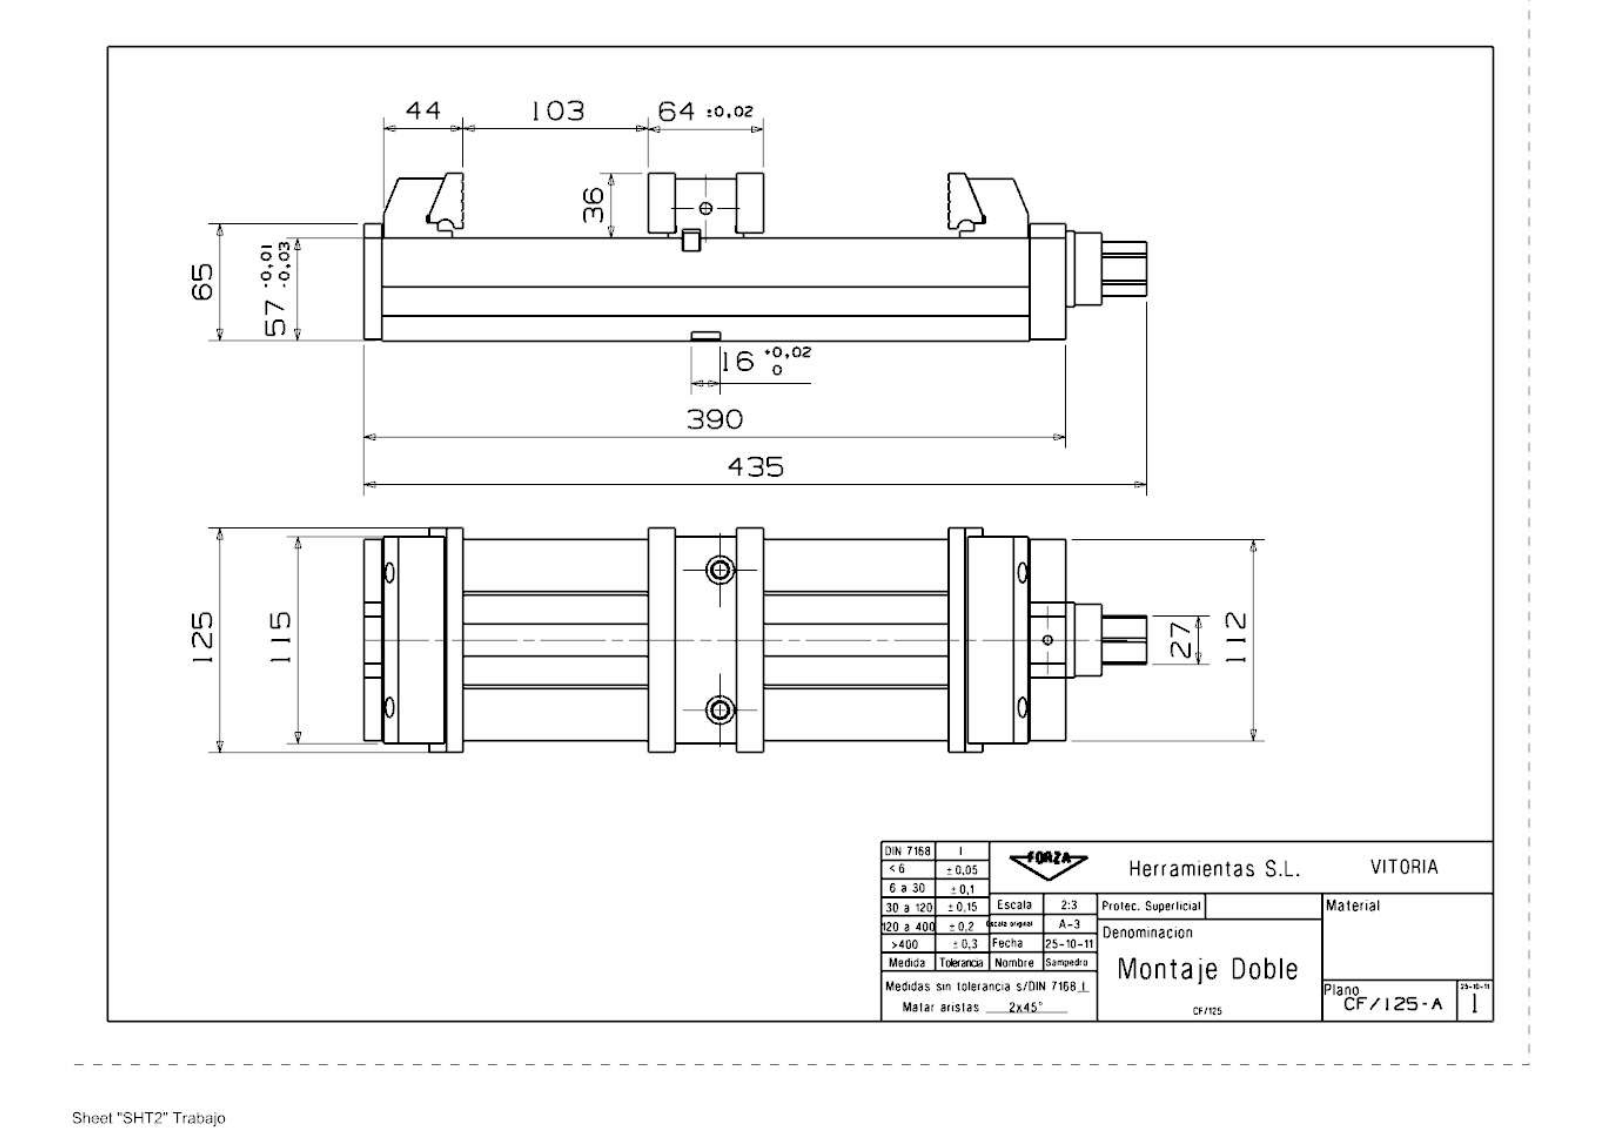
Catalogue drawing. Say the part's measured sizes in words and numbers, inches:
The part is named "CF_125_Mordaza". Its 3-D file was written by "SIEMENS PLM Software NX 9.0 (CONFIG_CONTROL_DESIGN)". It is 20 solids with 606 faces: 385 planar, 171 cylindrical and 50 other. Overall it measures 17.126 by 4.921 by 3.661 inches. Its volume is 145.5 cubic inches and its surface area 664.9 square inches. Round holes: 12 of diameter 0.204, 6 of diameter 0.315, 5 of diameter 0.275, 4 of diameter 0.295, 4 of diameter 0.346, 4 of diameter 0.413, 4 of diameter 0.453, 3 of diameter 0.24, 3 of diameter 0.433, 3 of diameter 0.63, 2 of diameter 0.128, 2 of diameter 0.135. Round bosses or shafts: 3 of diameter 1.102, 2 of diameter 0.945, 1 of diameter 1.654, 1 of diameter 1.575, 1 of diameter 1.181, 1 of diameter 0.866, 1 of diameter 0.709, 1 of diameter 0.512. Partial cylindrical surfaces (rounded edges, fillets, slot ends): 20 of radius 0.012, 8 of radius 0.059, 4 of radius 0.197, 4 of radius 0.394, 2 of radius 0.315. The main face-to-face distances are 2.244, 0.774, 1.47, 3.504, 0.906, 4.409, 1.22, 0.669, 0.728, 0.984. The hole center spacings are 2.953, 3.29, 2.267, 0.36, 0.362, 0.699, 1.56, 1.575.
